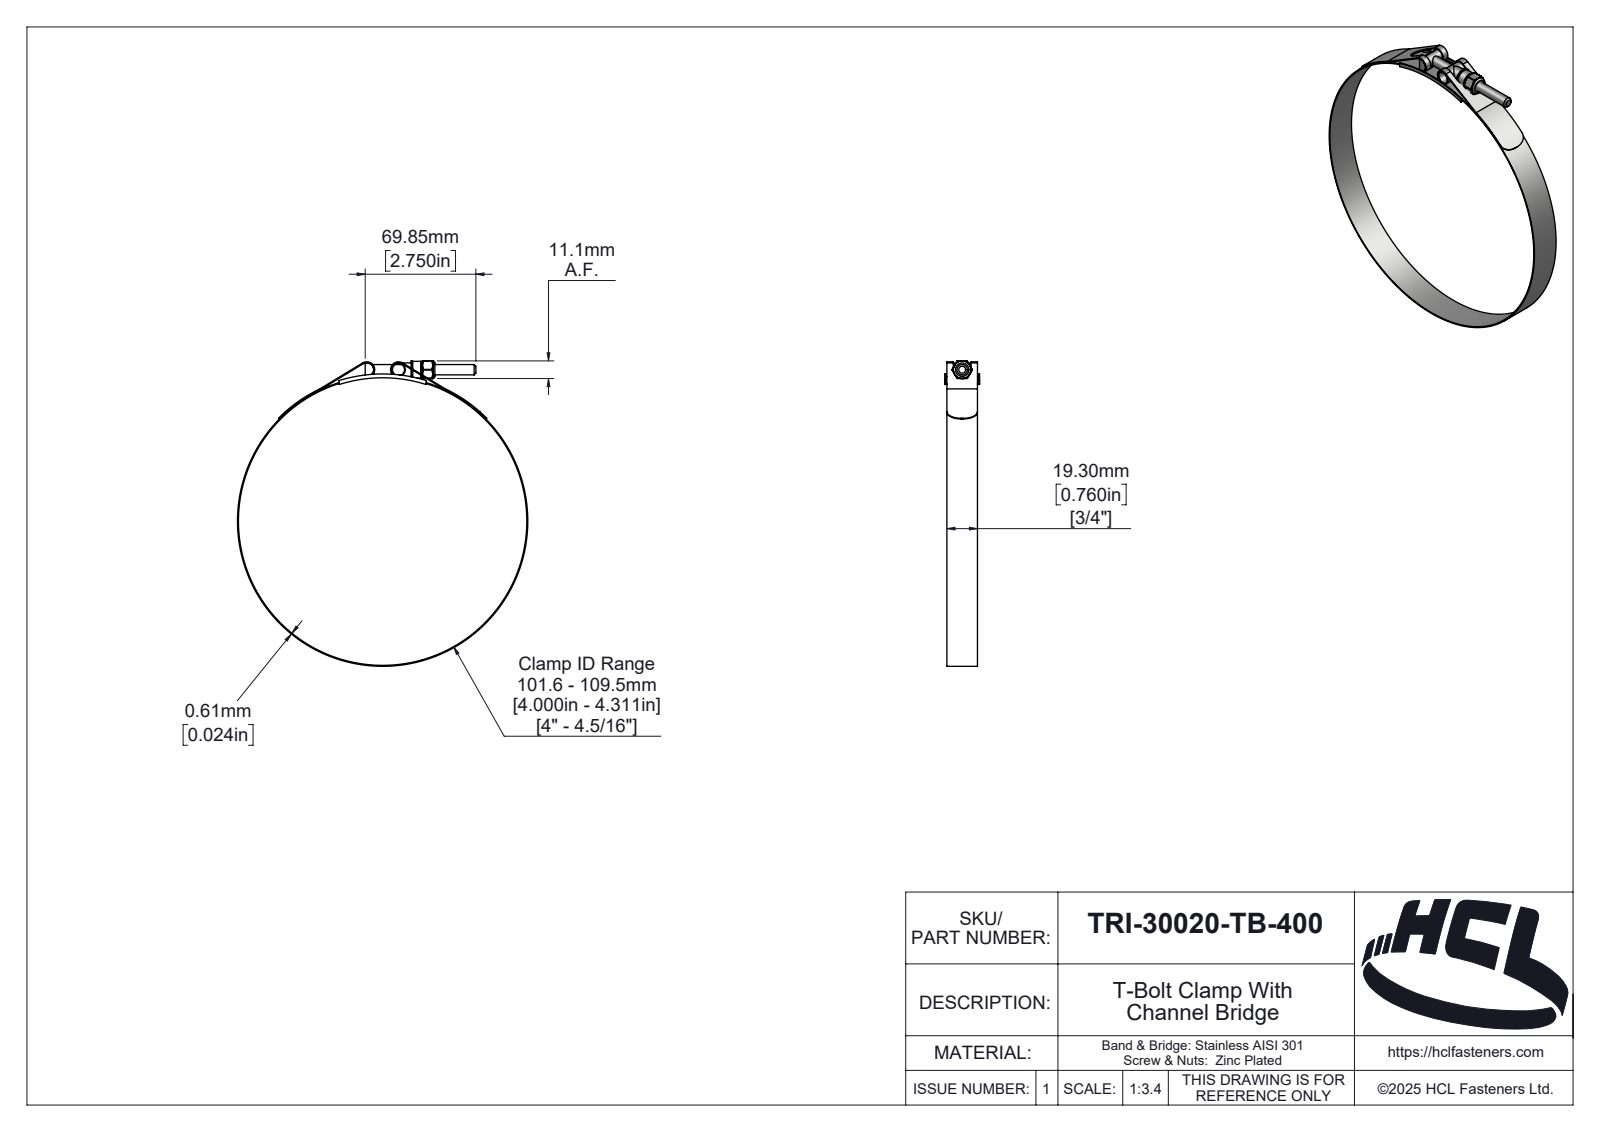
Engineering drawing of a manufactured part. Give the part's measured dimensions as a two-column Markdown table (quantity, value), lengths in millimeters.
| quantity | value |
| --- | --- |
| part name | TRI-30020-TB-400 |
| STEP written by | SolidWorks 2025 (AUTOMOTIVE_DESIGN) |
| units | millimeters |
| bodies | 6 solids, 330 faces (44 planar, 122 cylindrical, 164 other) |
| overall size | 192.81 × 183.22 × 22 |
| volume | 13 059 mm³ |
| surface area | 34 513 mm² |
| round holes (diameter × count) | 5.4 × 1, 6.35 × 1, 6.5 × 1, 7.58 × 1, 182 × 1 |
| round bosses / shafts (diameter × count) | 8.58 × 2, 183.22 × 1, 10.58 × 1 |
| partial cylindrical surfaces (radius × count) | 0.39 × 6, 0.5 × 2, 4.39 × 2, 5 × 2, 0.59 × 1, 2.42 × 1, 3.03 × 1, 3.19 × 1 |
| main face-to-face distances | 0.6, 19.3, 1.35, 20.65, 0.74, 0.61, 21.39, 20.04, 22, 20.78 |
| hole center spacings | 96 |
